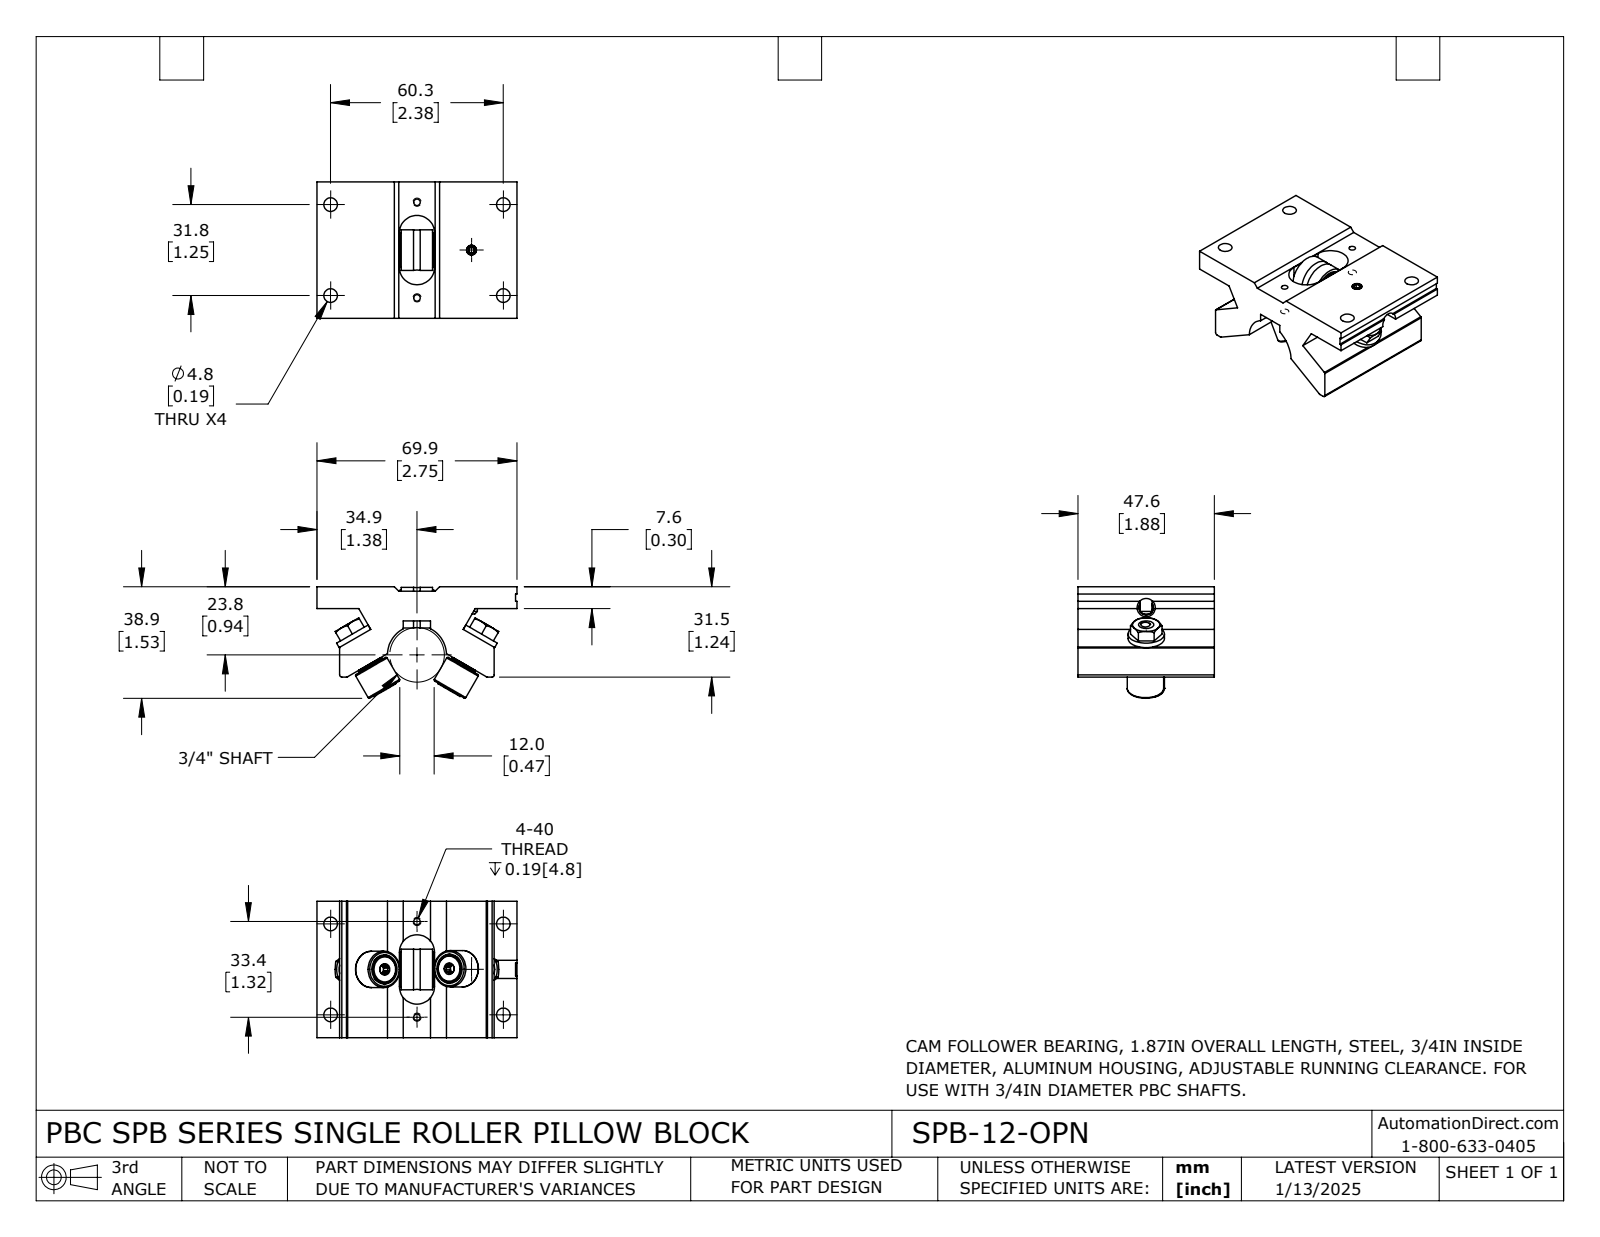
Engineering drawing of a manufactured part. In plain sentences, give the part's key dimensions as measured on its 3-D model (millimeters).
The part is named "SPB-12-OPN". Its 3-D file was written by "SolidWorks 2023 (CONFIG_CONTROL_DESIGN)". It is 9 solids with 306 faces: 127 planar, 99 cylindrical and 80 other. Overall it measures 69.9 by 47.6 by 38.9 millimeters. Its volume is 55 850 cubic millimeters and its surface area 20 370 square millimeters. Round holes: 4 of diameter 4.7, 2 of diameter 2.3, 2 of diameter 3.3, 2 of diameter 3.8, 2 of diameter 10.1, 1 of diameter 3.5, 1 of diameter 4, 1 of diameter 4.8, 1 of diameter 4.9, 1 of diameter 5, 1 of diameter 5, 1 of diameter 5.1. Round bosses or shafts: 3 of diameter 12.7, 2 of diameter 9.4, 1 of diameter 14.1, 1 of diameter 12.1, 1 of diameter 6.4, 1 of diameter 5.1, 1 of diameter 5, 1 of diameter 4.8. Partial cylindrical surfaces (rounded edges, fillets, slot ends): 4 of radius 0.8, 2 of radius 0.4, 2 of radius 6.2, 1 of radius 10.3. The main face-to-face distances are 10.3, 7.6, 47.6, 7.9, 61.9, 54, 6.1, 1.5, 28.8, 41.1. The hole center spacings are 30.2, 44.4, 25.3, 51.7, 60.3, 68.2, 19.4, 19.4.
